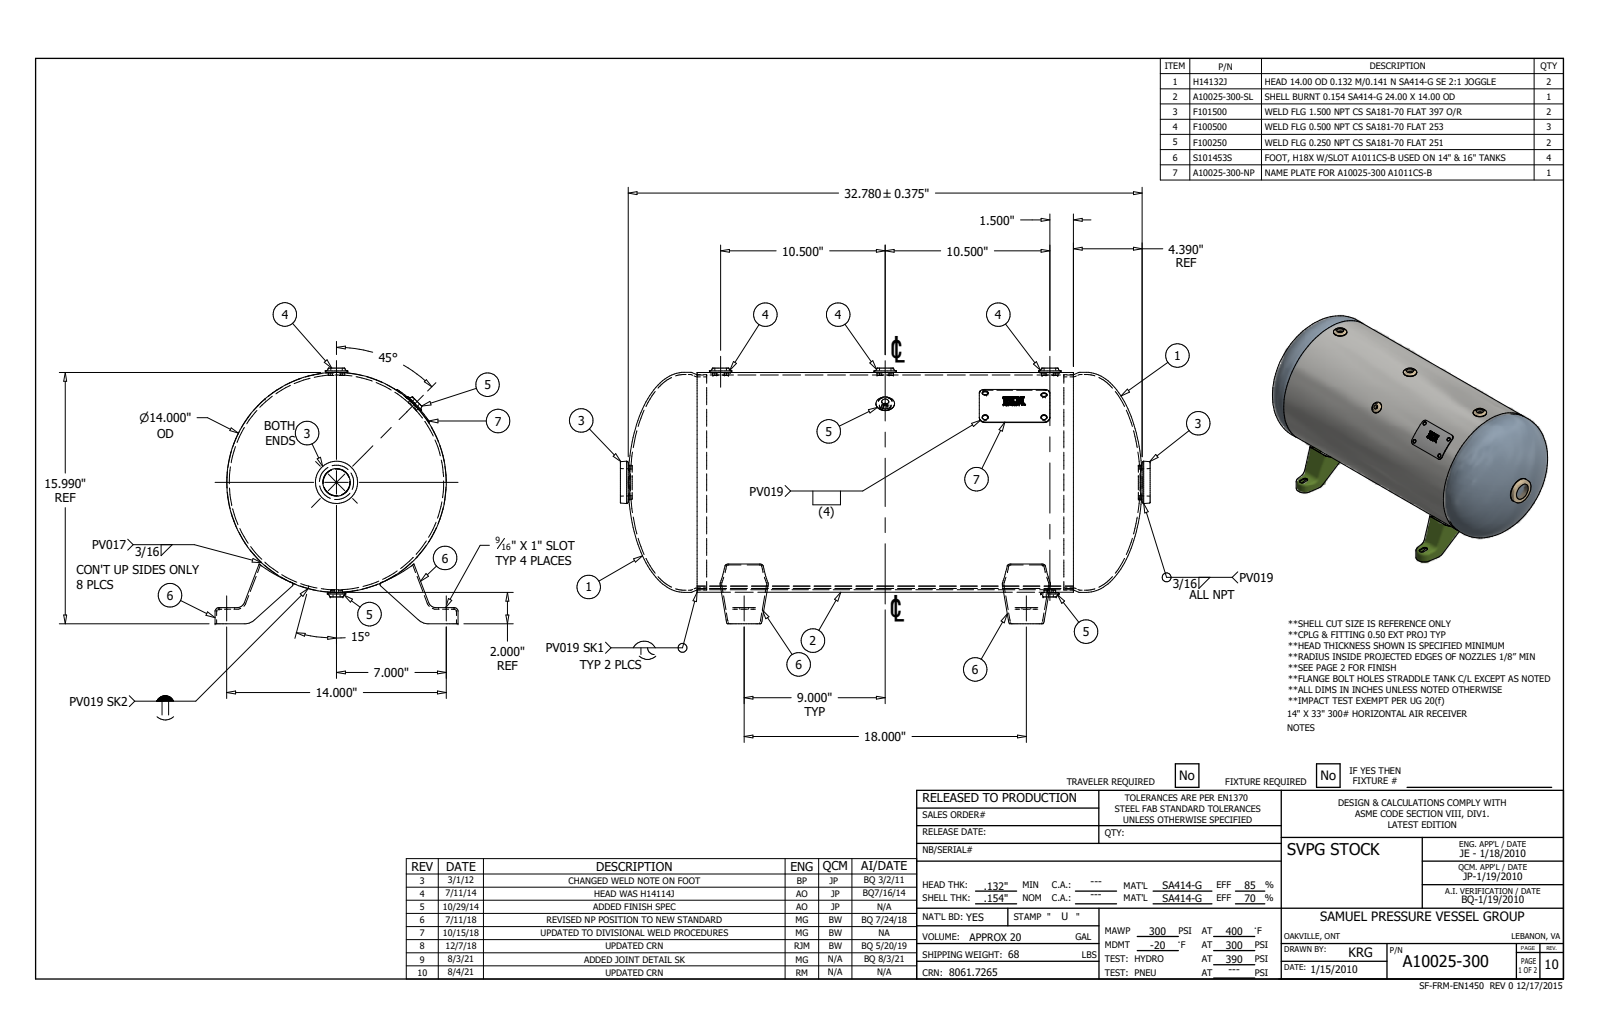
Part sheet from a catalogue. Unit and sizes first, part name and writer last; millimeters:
Units: millimetres
Overall size (bounding box): 858.01 × 413.29 × 393.7
Round holes (diameter × count): ⌀9.52 ×4, ⌀12.7 ×3, ⌀18.64 ×3, ⌀6.35 ×2, ⌀11.46 ×2, ⌀43.26 ×1, ⌀340.82 ×1, ⌀347.28 ×1, ⌀348.44 ×1, ⌀355.6 ×1
Round bosses / shafts (diameter × count): ⌀26.99 ×3, ⌀355.1 ×1, ⌀347.98 ×1, ⌀55.56 ×1
Partial cylindrical surfaces — rounded edges, fillets, slot ends (radius × count): R3.81 ×16, R6.35 ×16, R7.14 ×8, R9.53 ×4, R20.05 ×4, R22.59 ×4, R3.17 ×2, R12.7 ×2
Main face-to-face distances: 2.54, 451.71, 95.61, 454.25, 449.17, 95.59, 98.13, 98.15, 547.32, 93.07
Hole centre spacings: 266.7, 50.71, 55.47, 95.25, 95.37, 107.91, 110.23, 533.4
Volume: 4 115 000 mm³ · Surface area: 2 249 000 mm²
Bodies: 28 solids, 695 faces (352 planar, 139 cylindrical, 204 other)
Part name (STEP PRODUCT): A10025-300; A10025-300-SL; H14132J; F101500 (+4 more)
STEP written by: Autodesk Inventor 2017 (AUTOMOTIVE_DESIGN)
